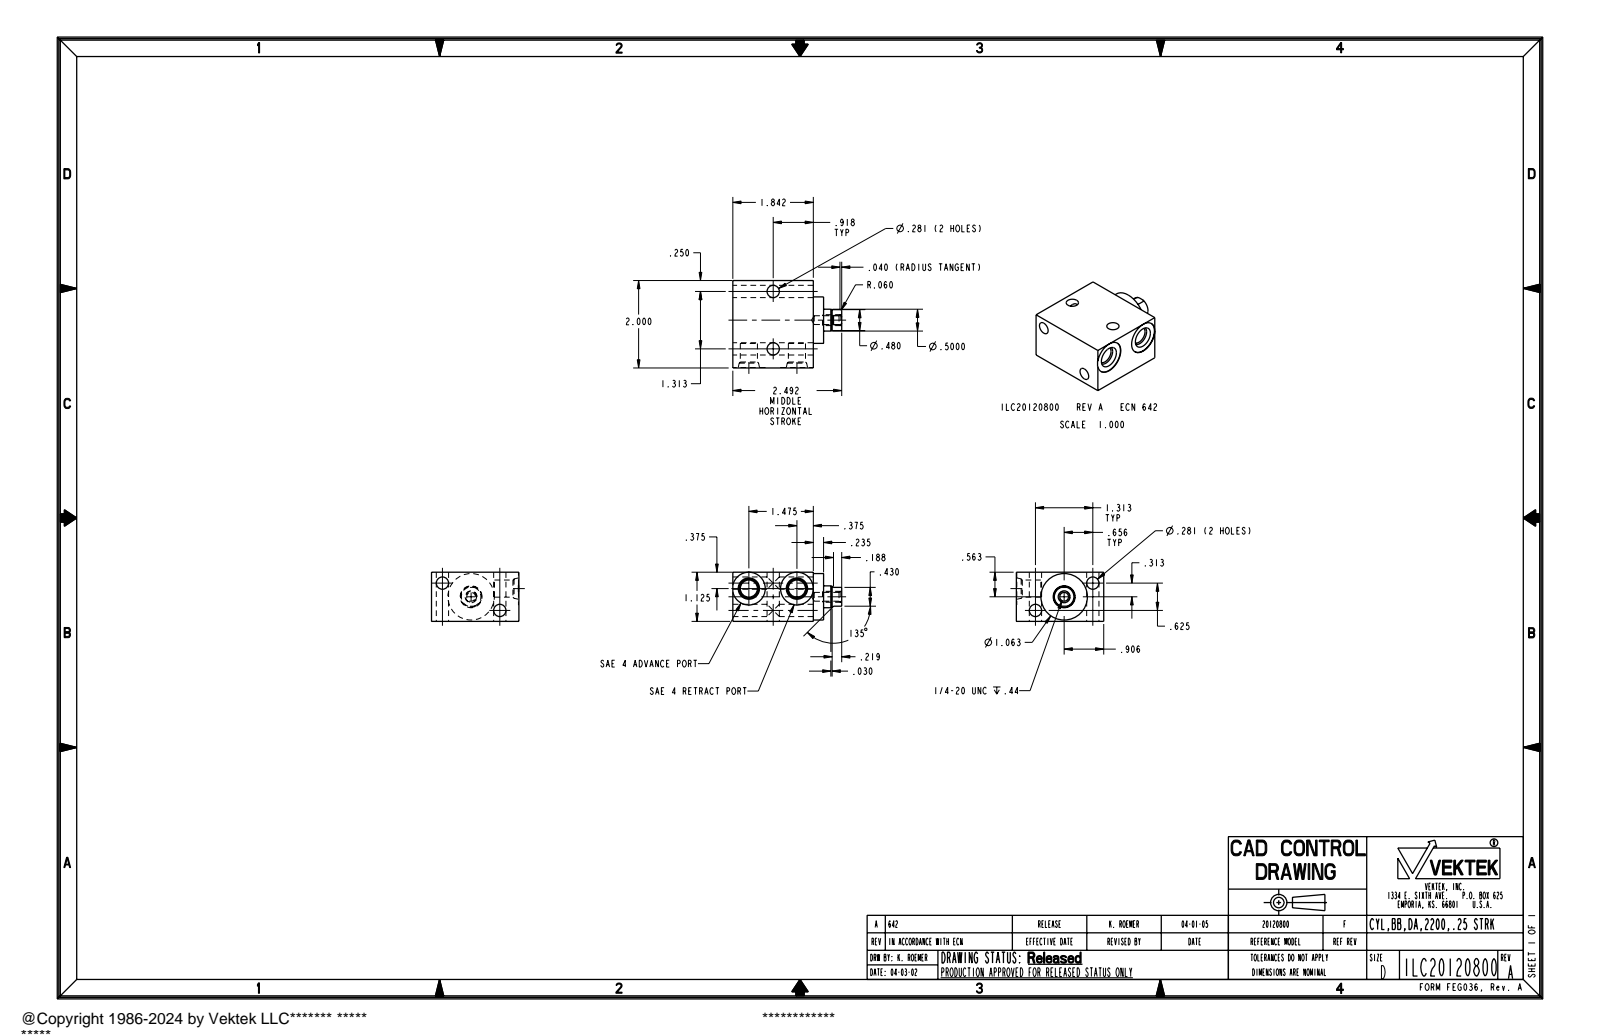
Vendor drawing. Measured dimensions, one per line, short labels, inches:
name: ILC20120800
written by: PRO/ENGINEER BY PARAMETRIC TECHNOLOGY CORPORATION, 2004290 (AUTOMOTIVE_DESIGN_CC2)
unit: in
bodies: 1 solid, 68 faces (19 planar, 33 cylindrical, 16 other)
size: 2.492 × 2 × 1.125
volume: 3.917 in³; area: 23.6 in²
holes: 4× ⌀0.281, 2× ⌀0.392, 2× ⌀0.75, 1× ⌀0.201
bosses: 1× ⌀1.063, 1× ⌀0.5, 1× ⌀0.48, 1× ⌀0.25
face distances: 1.125, 1.842, 2, 0.235, 2.077, 1.99, 0.56, 0.55, 1.44, 0.415
hole spacings: 0.727, 0.727, 1.1, 1.313, 1.454
